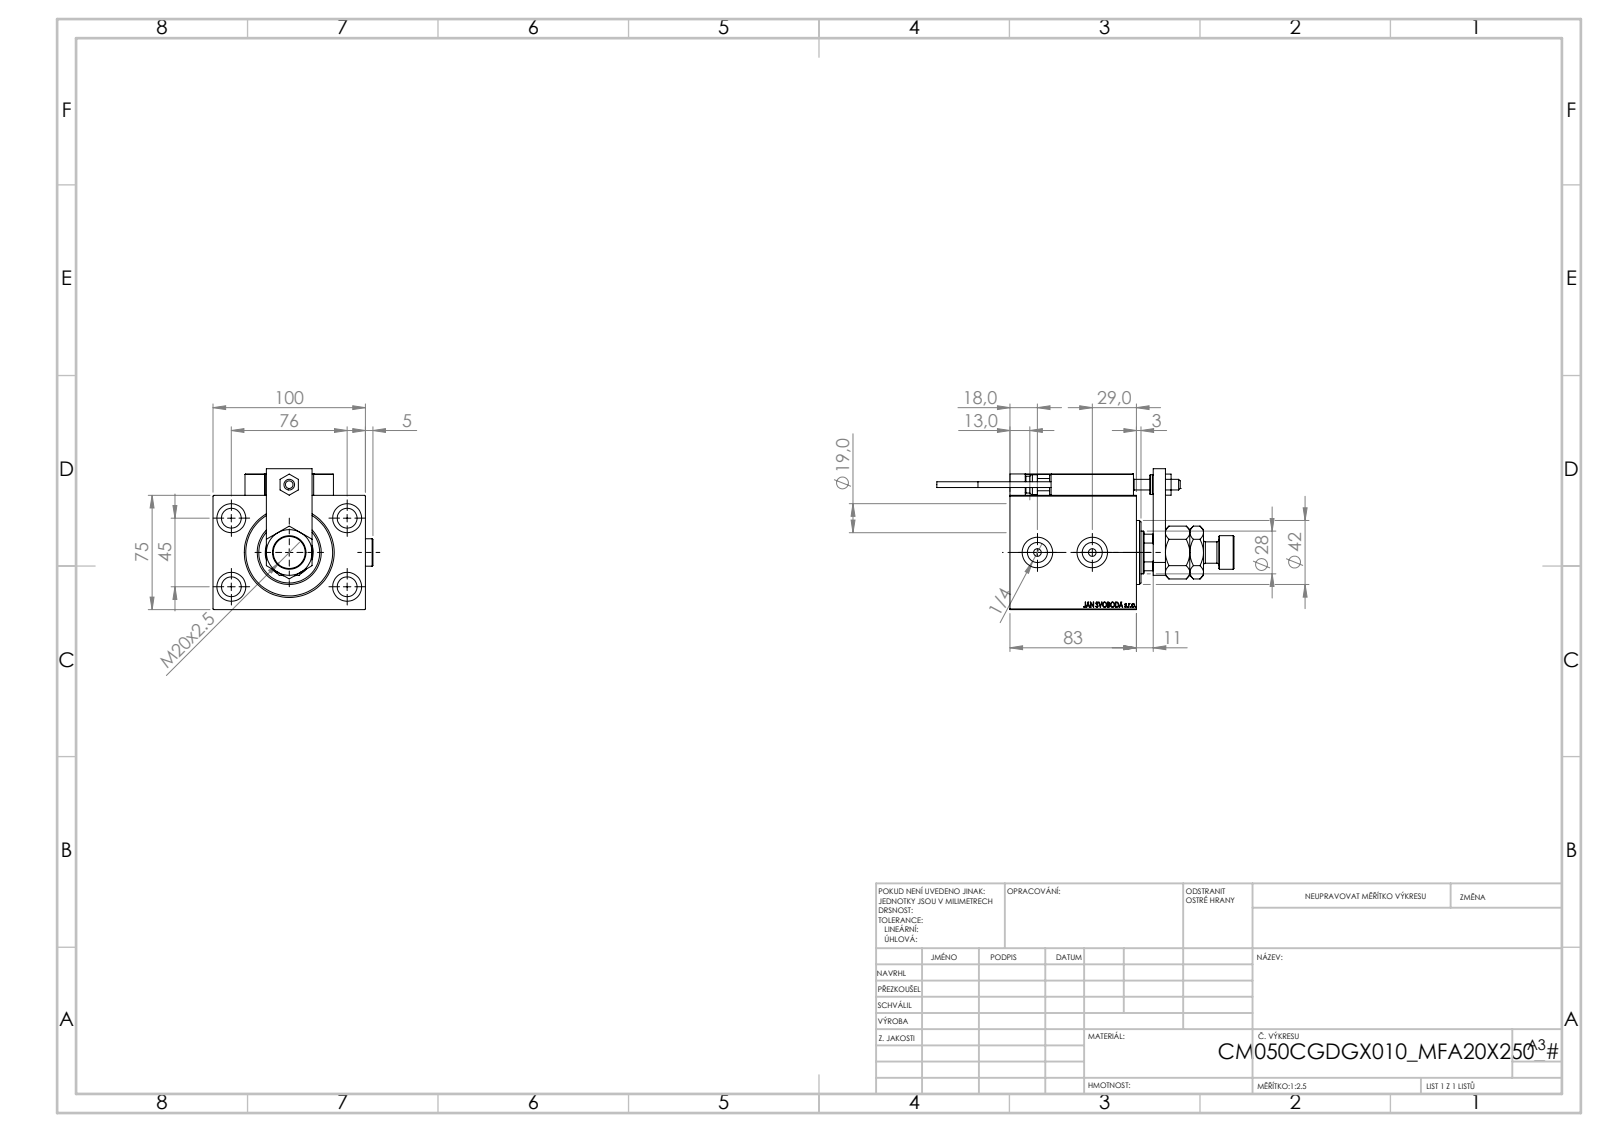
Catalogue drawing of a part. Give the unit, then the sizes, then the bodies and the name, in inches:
Units: inches
Overall size (bounding box): 7.677 × 4.13 × 3.642
Round holes (diameter × count): ⌀0.315 ×5, ⌀0.126 ×4, ⌀0.157 ×4, ⌀0.197 ×4, ⌀0.512 ×4, ⌀0.748 ×4, ⌀0.787 ×3, ⌀0.518 ×2, ⌀0.276 ×1, ⌀0.728 ×1, ⌀1.102 ×1, ⌀1.24 ×1
Round bosses / shafts (diameter × count): ⌀0.709 ×2, ⌀0.197 ×2, ⌀0.15 ×2, ⌀1.654 ×1, ⌀0.866 ×1, ⌀0.551 ×1, ⌀0.512 ×1, ⌀0.433 ×1
Partial cylindrical surfaces — rounded edges, fillets, slot ends (radius × count): R0.012 ×30, R0.118 ×2, R0.531 ×1
Main face-to-face distances: 2.953, 3.937, 1.26, 3.268, 2.008, 0.551, 0.315, 2.756, 0.512, 0.748
Hole centre spacings: 1.739, 0.448, 0.787, 1.165, 1.169, 1.38, 1.42, 1.628
Volume: 38 in³ · Surface area: 195.3 in²
Bodies: 26 solids, 1389 faces (611 planar, 208 cylindrical, 570 other)
Part name (STEP PRODUCT): ALLEN BOLT D8; SWITCH_X_FRONT_BACK; TYC_L79; ZARAZKA (+8 more)
STEP written by: SolidWorks 2019 (CONFIG_CONTROL_DESIGN)
